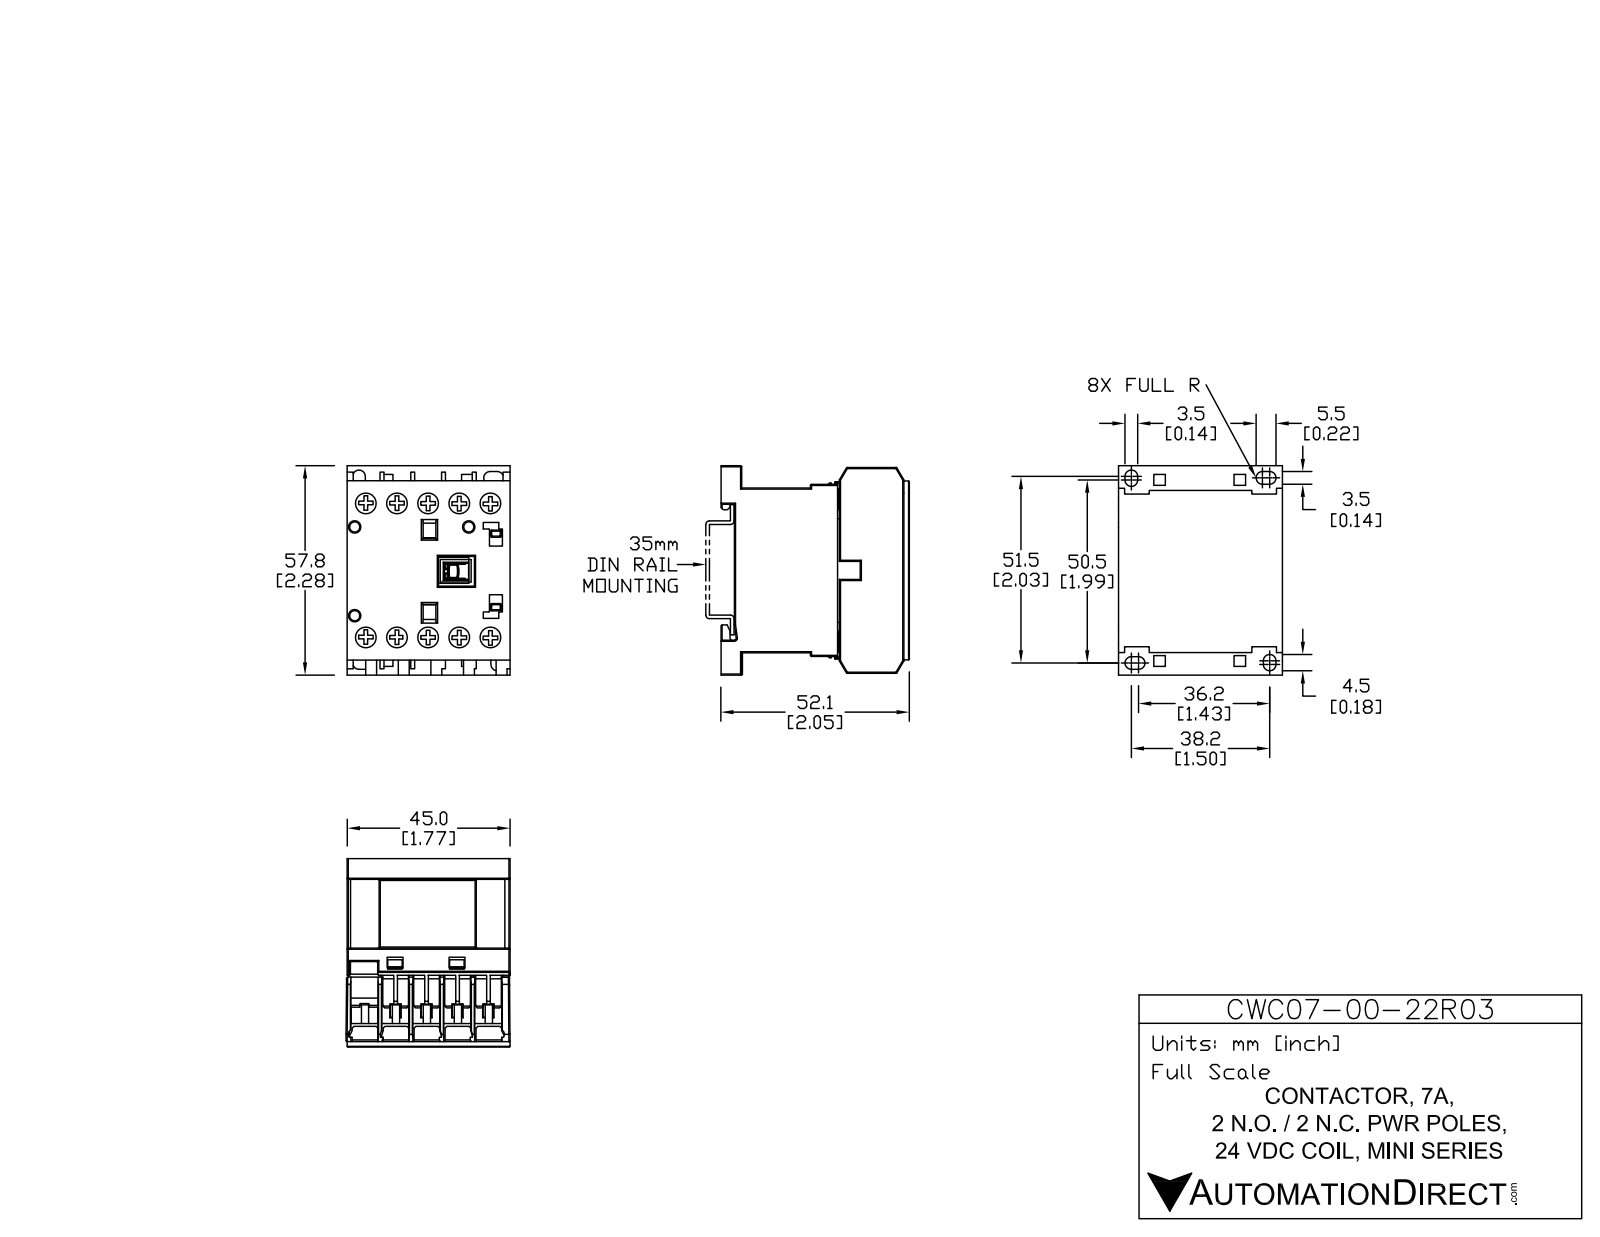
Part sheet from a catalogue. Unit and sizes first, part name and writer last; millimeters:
Units: millimetres
Overall size (bounding box): 58.04 × 52.12 × 45.75
Round holes (diameter × count): ⌀6.2 ×10, ⌀2.8 ×3
Round bosses / shafts (diameter × count): ⌀5.9 ×10
Partial cylindrical surfaces — rounded edges, fillets, slot ends (radius × count): R0.3 ×20, R1.72 ×6, R1.73 ×2, R0.32 ×1, R0.42 ×1, R0.55 ×1
Main face-to-face distances: 8.25, 45.5, 1.25, 16.5, 9.5, 5.5, 17.75, 5.13, 10.63, 7
Hole centre spacings: 8.55, 37.94, 17.1, 40.72, 36.96, 25.65, 44.99, 6.91
Volume: 97 133 mm³ · Surface area: 30 437 mm²
Bodies: 15 solids, 535 faces (445 planar, 90 cylindrical, 0 other)
Part name (STEP PRODUCT): CWC07-00-22R03
STEP written by: SolidWorks 2013 (AUTOMOTIVE_DESIGN)
